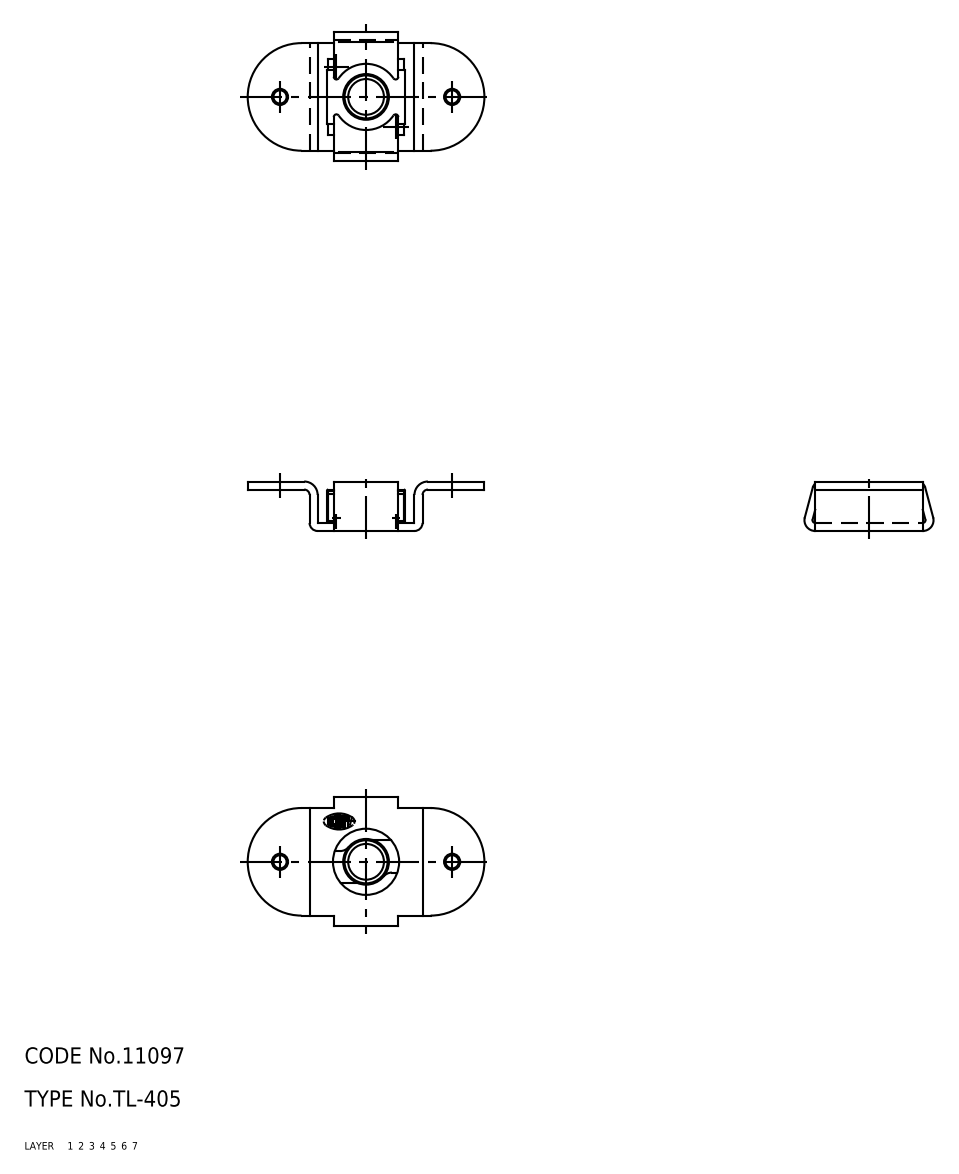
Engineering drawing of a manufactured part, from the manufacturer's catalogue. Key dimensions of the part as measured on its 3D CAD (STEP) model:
Part name (STEP PRODUCT): ブラケット; ibg^TL_405; TL_405
STEP written by: SolidWorks 2015 (AUTOMOTIVE_DESIGN)
Units: millimetres
Bodies: 3 solids, 159 faces (66 planar, 77 cylindrical, 16 other)
Overall size (bounding box): 44 × 24 × 9.2
Volume: 2 713 mm³ · Surface area: 4 455 mm²
Round holes (diameter × count): ⌀1.8 ×2, ⌀2.46 ×2, ⌀6.65 ×1, ⌀8.5 ×1, ⌀12.3 ×1
Partial cylindrical surfaces — rounded edges, fillets, slot ends (radius × count): R0.5 ×10, R1 ×6, R1.5 ×6, R2 ×6, R0.2 ×5, R0.3 ×2, R2.5 ×2, R4.25 ×2
Main face-to-face distances: 1.5, 7.7, 9.2, 6.2, 19.5, 14.25, 14.05, 14.3, 3, 2
Hole centre spacings: 7.78, 11.85, 16, 22.19, 15.56, 32
